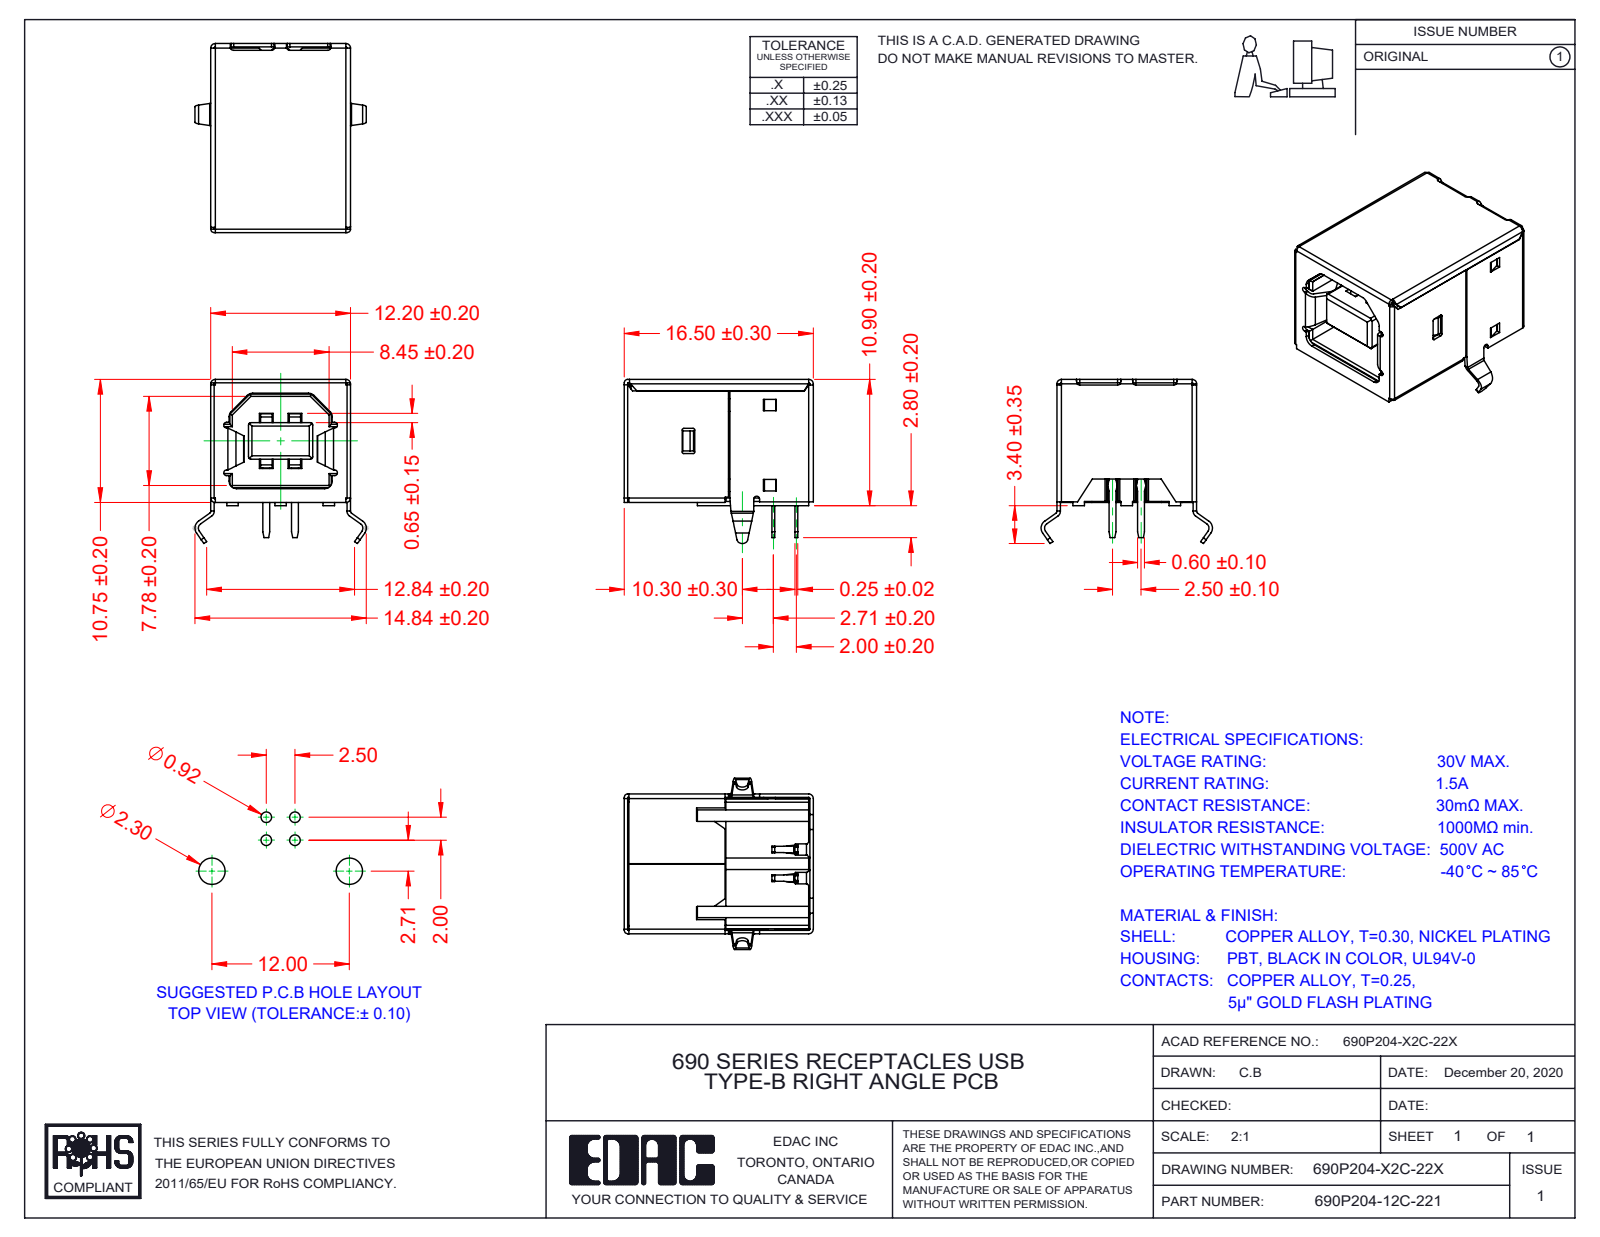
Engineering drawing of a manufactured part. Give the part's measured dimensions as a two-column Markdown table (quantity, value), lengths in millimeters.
| quantity | value |
| --- | --- |
| part name | 690P204-12C-221; CONTACT 690P204-X2C-22X; CONTACT01 690P204-X2C-22X; SHELL 690P204-X2C-22X (+1 more) |
| STEP written by | SolidWorks 2020 (AUTOMOTIVE_DESIGN) |
| units | millimeters |
| bodies | 6 solids, 713 faces (549 planar, 145 cylindrical, 19 other) |
| overall size | 16.5 × 14.96 × 14.33 |
| volume | 1 279 mm³ |
| surface area | 3 559 mm² |
| partial cylindrical surfaces (radius × count) | 0.1 × 21, 0.3 × 21, 0.25 × 7, 0.4 × 7, 0.2 × 6, 0.6 × 6, 0.66 × 6, 0.85 × 6 |
| main face-to-face distances | 11.9, 10.45, 0.43, 11.77, 11.47, 10.15, 11.6, 12.2, 16.2, 8.6 |
